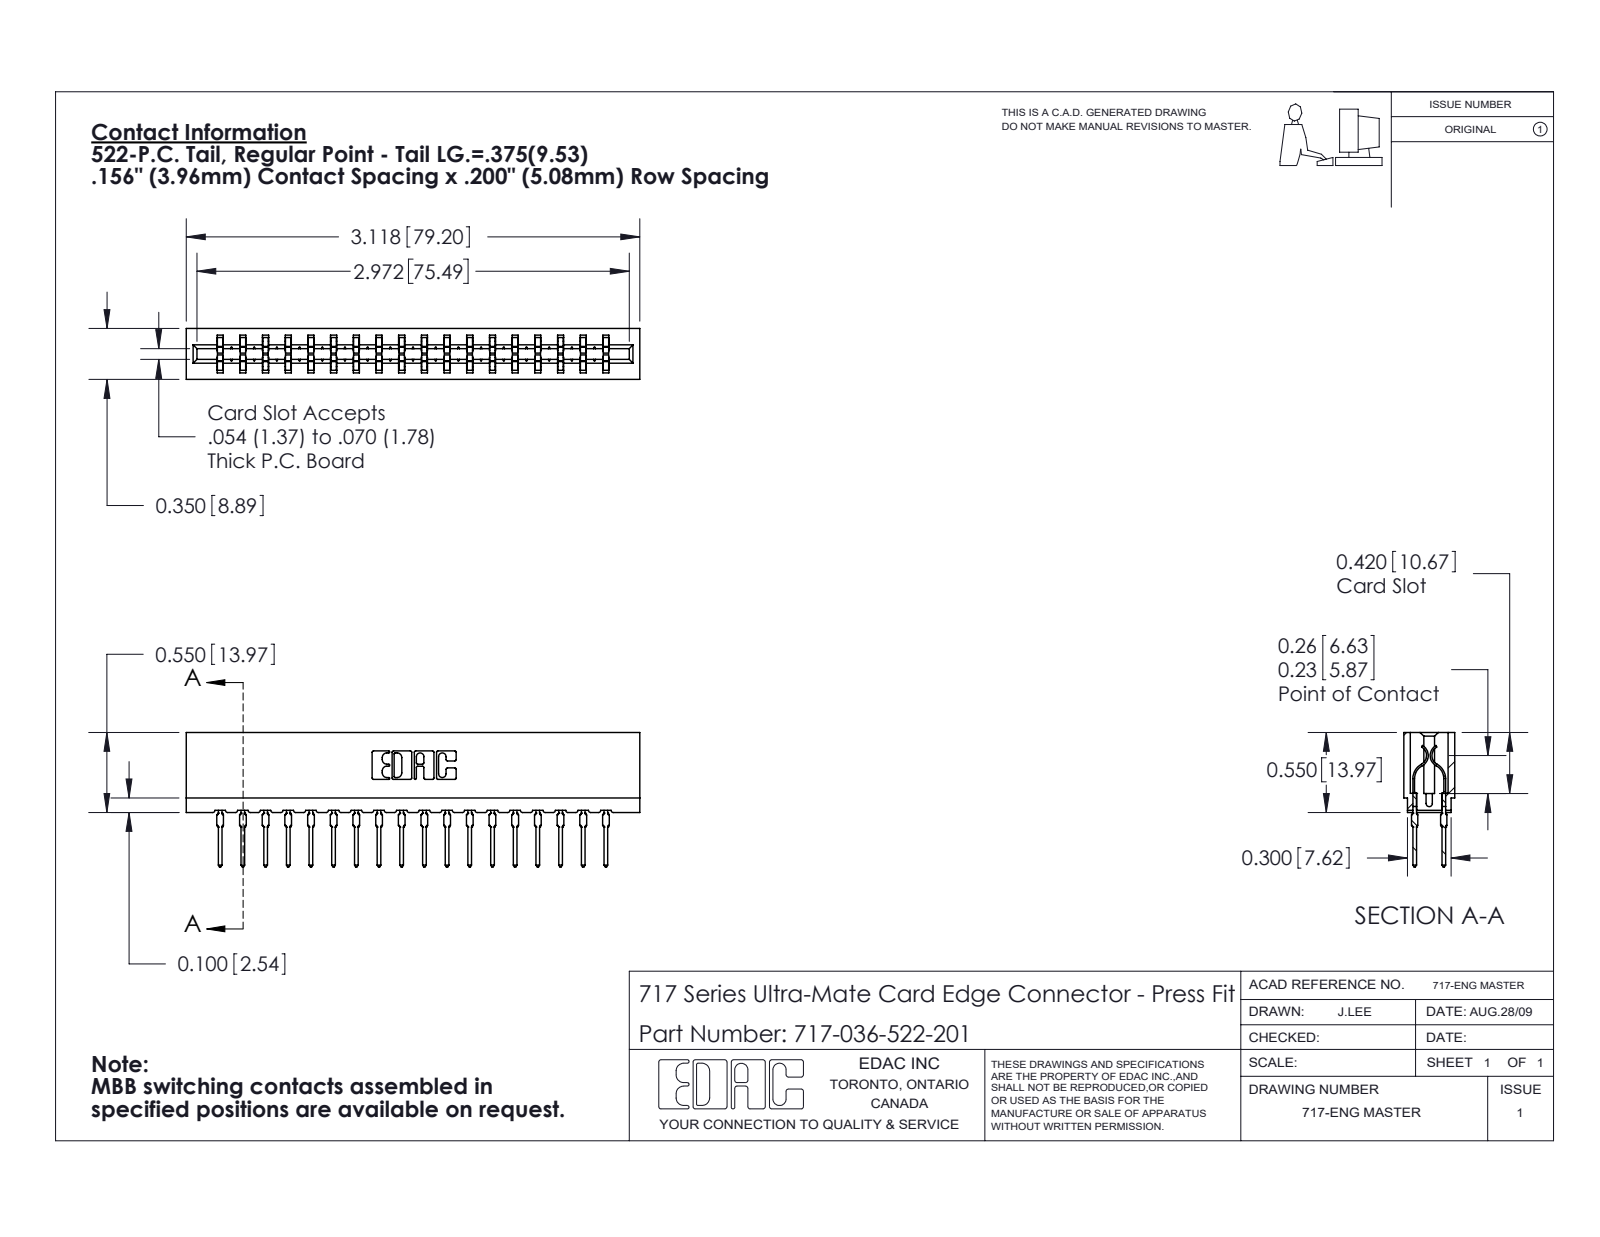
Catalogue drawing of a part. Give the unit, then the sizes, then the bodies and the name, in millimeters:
Units: millimetres
Overall size (bounding box): 79.2 × 23.5 × 8.9
Partial cylindrical surfaces — rounded edges, fillets, slot ends (radius × count): R0.5 ×72, R0.4 ×36, R0.3 ×22, R0.1 ×8, R0.3 ×8, R0.2 ×6, R0.8 ×6, R0.7 ×3
Main face-to-face distances: 5.4, 3.5, 8.9, 4, 1.6, 7.3, 1.9, 3.8, 15.8, 1.9
Volume: 7 000 mm³ · Surface area: 10 530 mm²
Bodies: 37 solids, 3334 faces (1728 planar, 670 cylindrical, 936 other)
Part name (STEP PRODUCT): 745-292-001_522; 717 Part_Insulator Option - 06; 717-036-522-201
STEP written by: SolidWorks 2020 (CONFIG_CONTROL_DESIGN)
